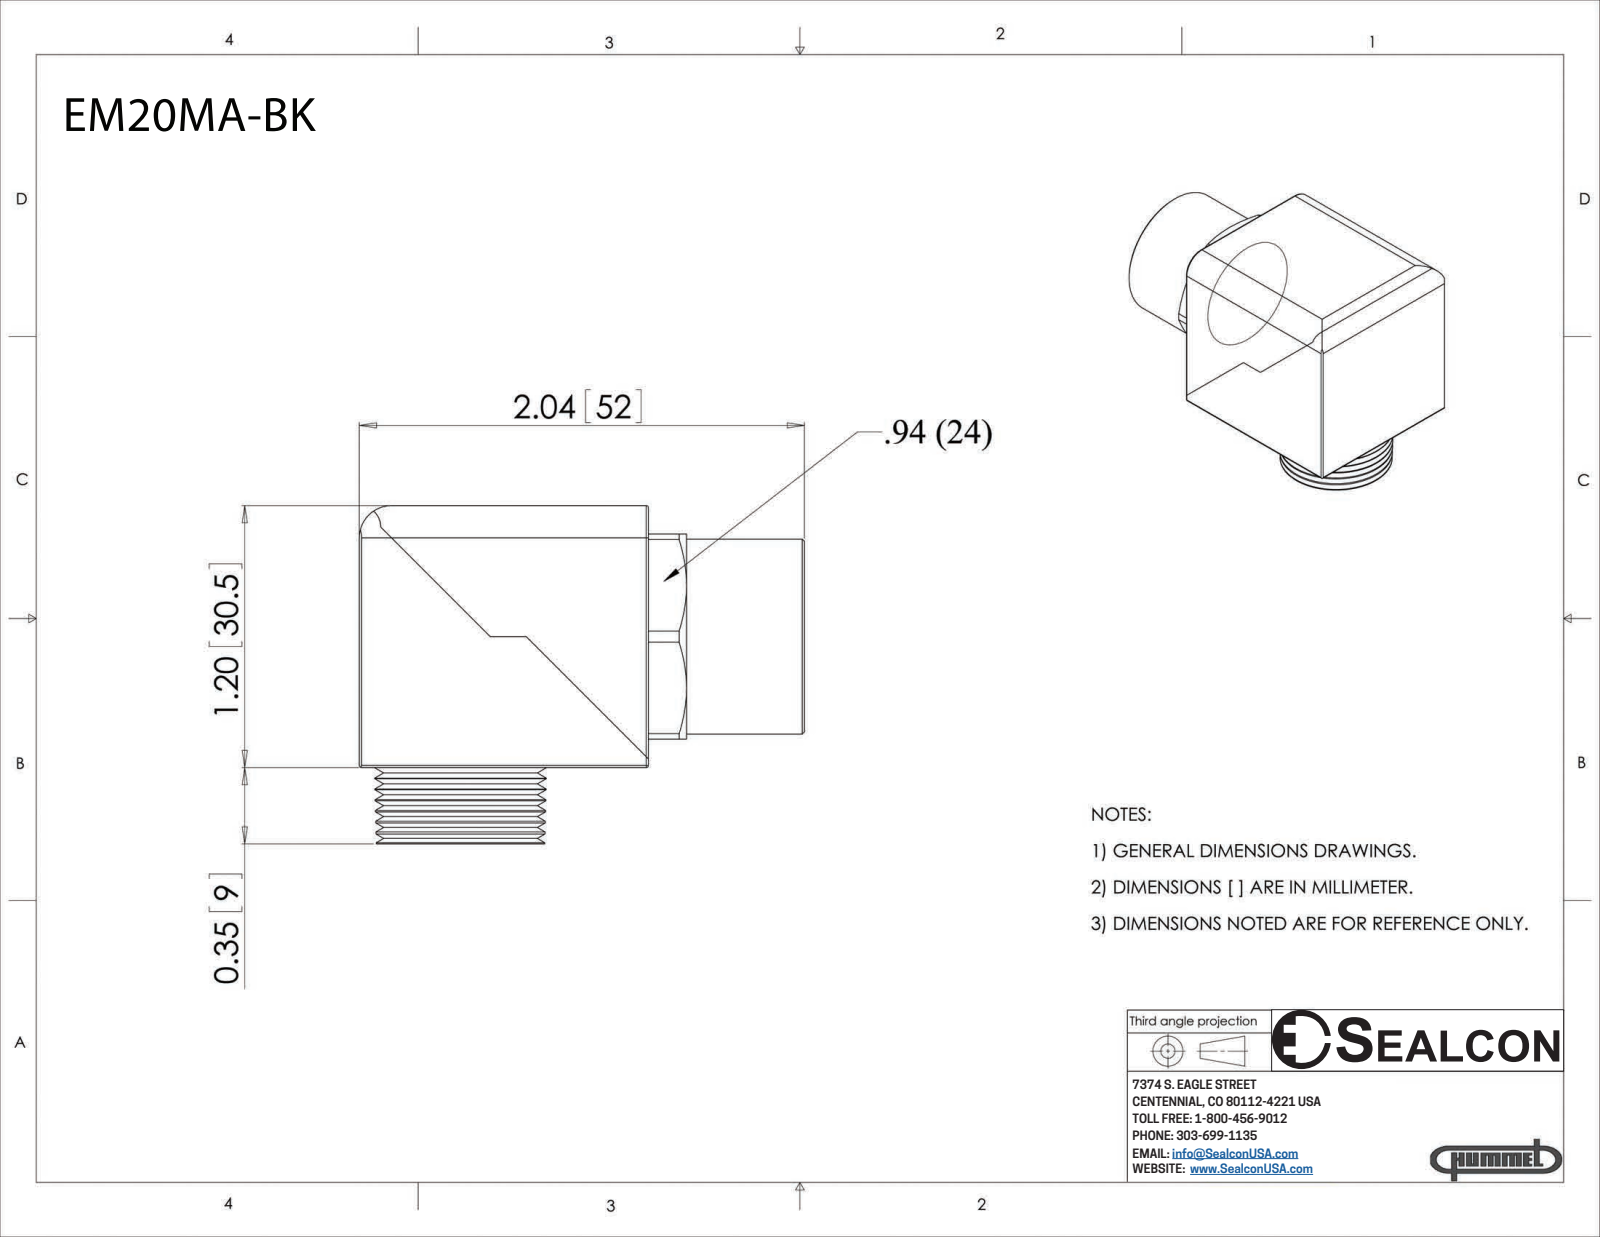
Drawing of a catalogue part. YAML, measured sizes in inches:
part_name: "EM20MA-BK"
step_written_by: "SolidWorks 2007 (AUTOMOTIVE_DESIGN)"
units: inches
bodies: {solids: 2, faces: 126, planar: 31, cylindrical: 34, other: 61}
overall_size: [2.04, 1.55, 1.2]
volume: 1.949
surface_area: 20.42
round_holes:
  - {diameter: 0.434, count: 2}
  - {diameter: 0.79, count: 1}
round_bosses_or_shafts:
  - {diameter: 0.893, count: 1}
partial_cylinders:
  - {radius: 0.01, count: 7}
  - {radius: 0.147, count: 3}
  - {radius: 0.098, count: 1}
  - {radius: 0.529, count: 1}
face_to_face_distances: [1.2, 0.117, 1.325, 0.6, 0.175, 1.5, 0.35, 1.55, 0.95, 0.94]
